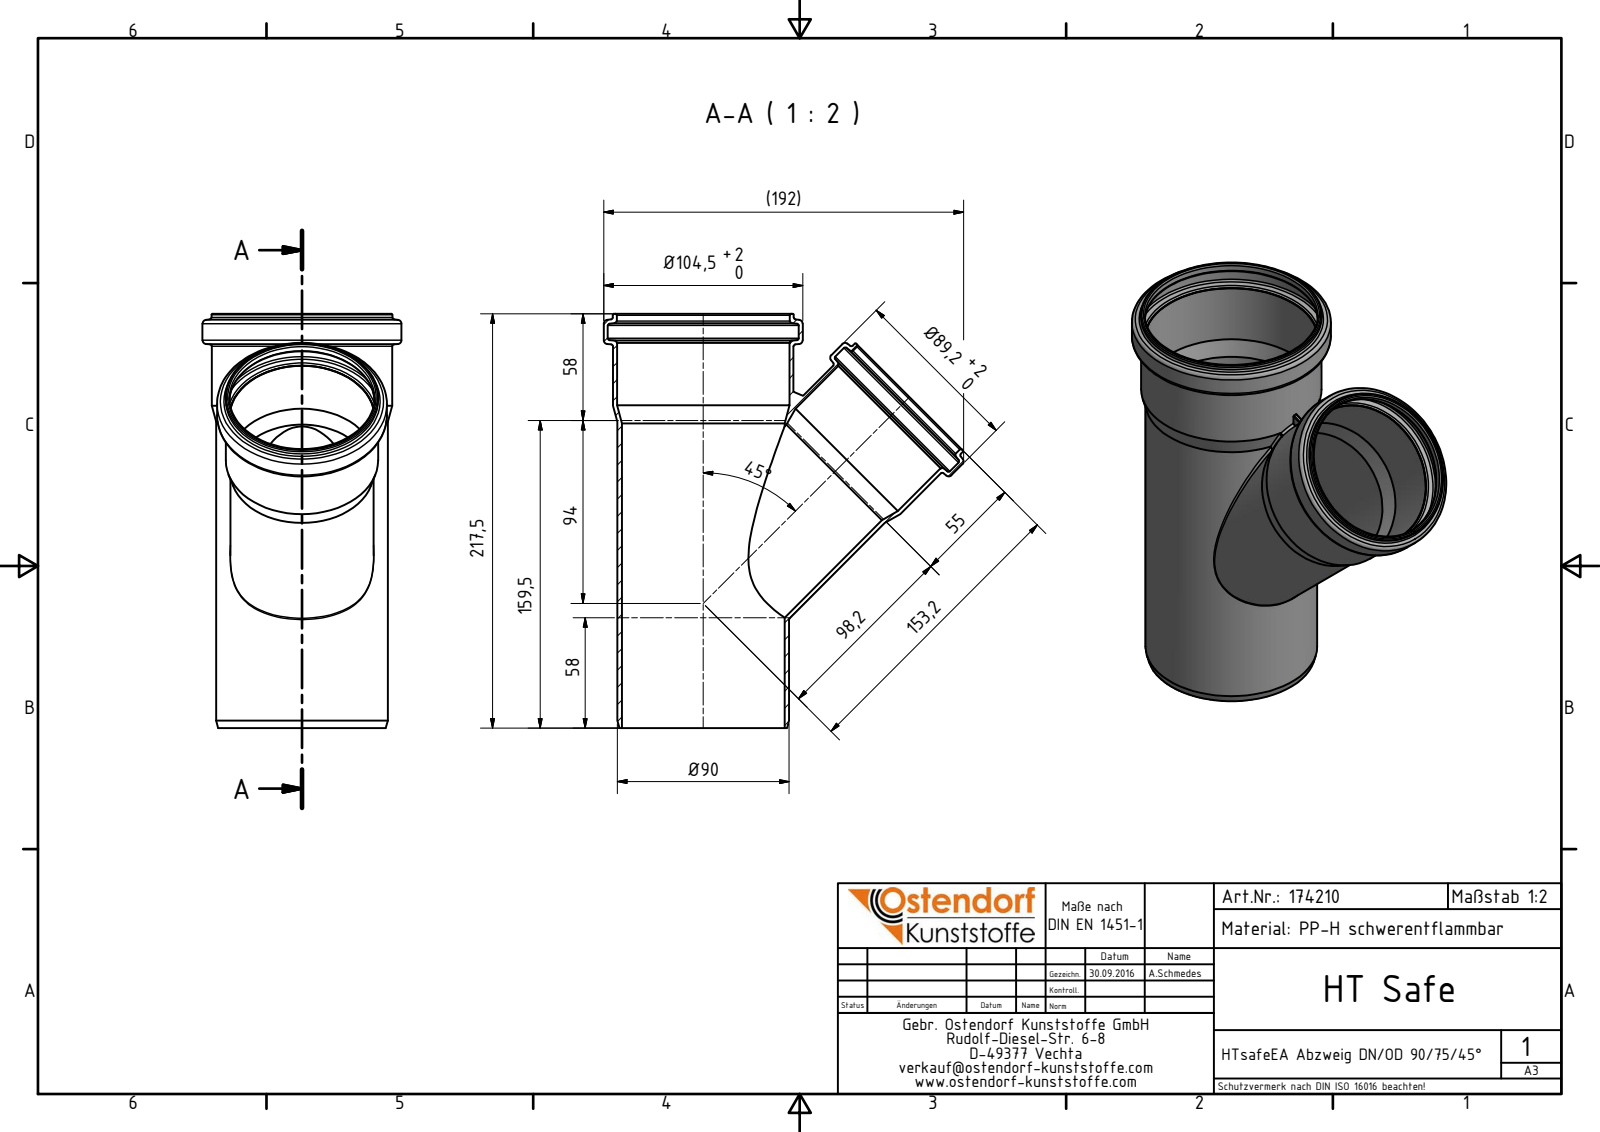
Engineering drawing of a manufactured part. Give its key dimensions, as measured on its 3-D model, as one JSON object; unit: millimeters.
{"part_name": "174210 HTsafeEA DN_OD 90_75_45°", "step_written_by": "Autodesk Inventor 2016 (AUTOMOTIVE_DESIGN)", "units": "millimeters", "bodies": {"solids": 1, "faces": 68, "planar": 8, "cylindrical": 20, "other": 40}, "overall_size": [217.5, 188.97, 104.5], "volume_mm3": 185566, "surface_area_mm2": 167617, "round_holes": [[71, 1], [76, 1], [76.3, 1], [85.2, 1], [85.4, 1], [90.5, 1], [90.8, 1], [100.3, 1]], "round_bosses_or_shafts": [[104.5, 1], [95, 1], [94.7, 1], [90.2, 1], [89.2, 1], [80.3, 1], [80, 1], [75.2, 1]], "partial_cylinders_radius": [[0.5, 2]], "face_to_face_distances": [217.5, 202.29, 15.21, 14.9, 2.4]}
